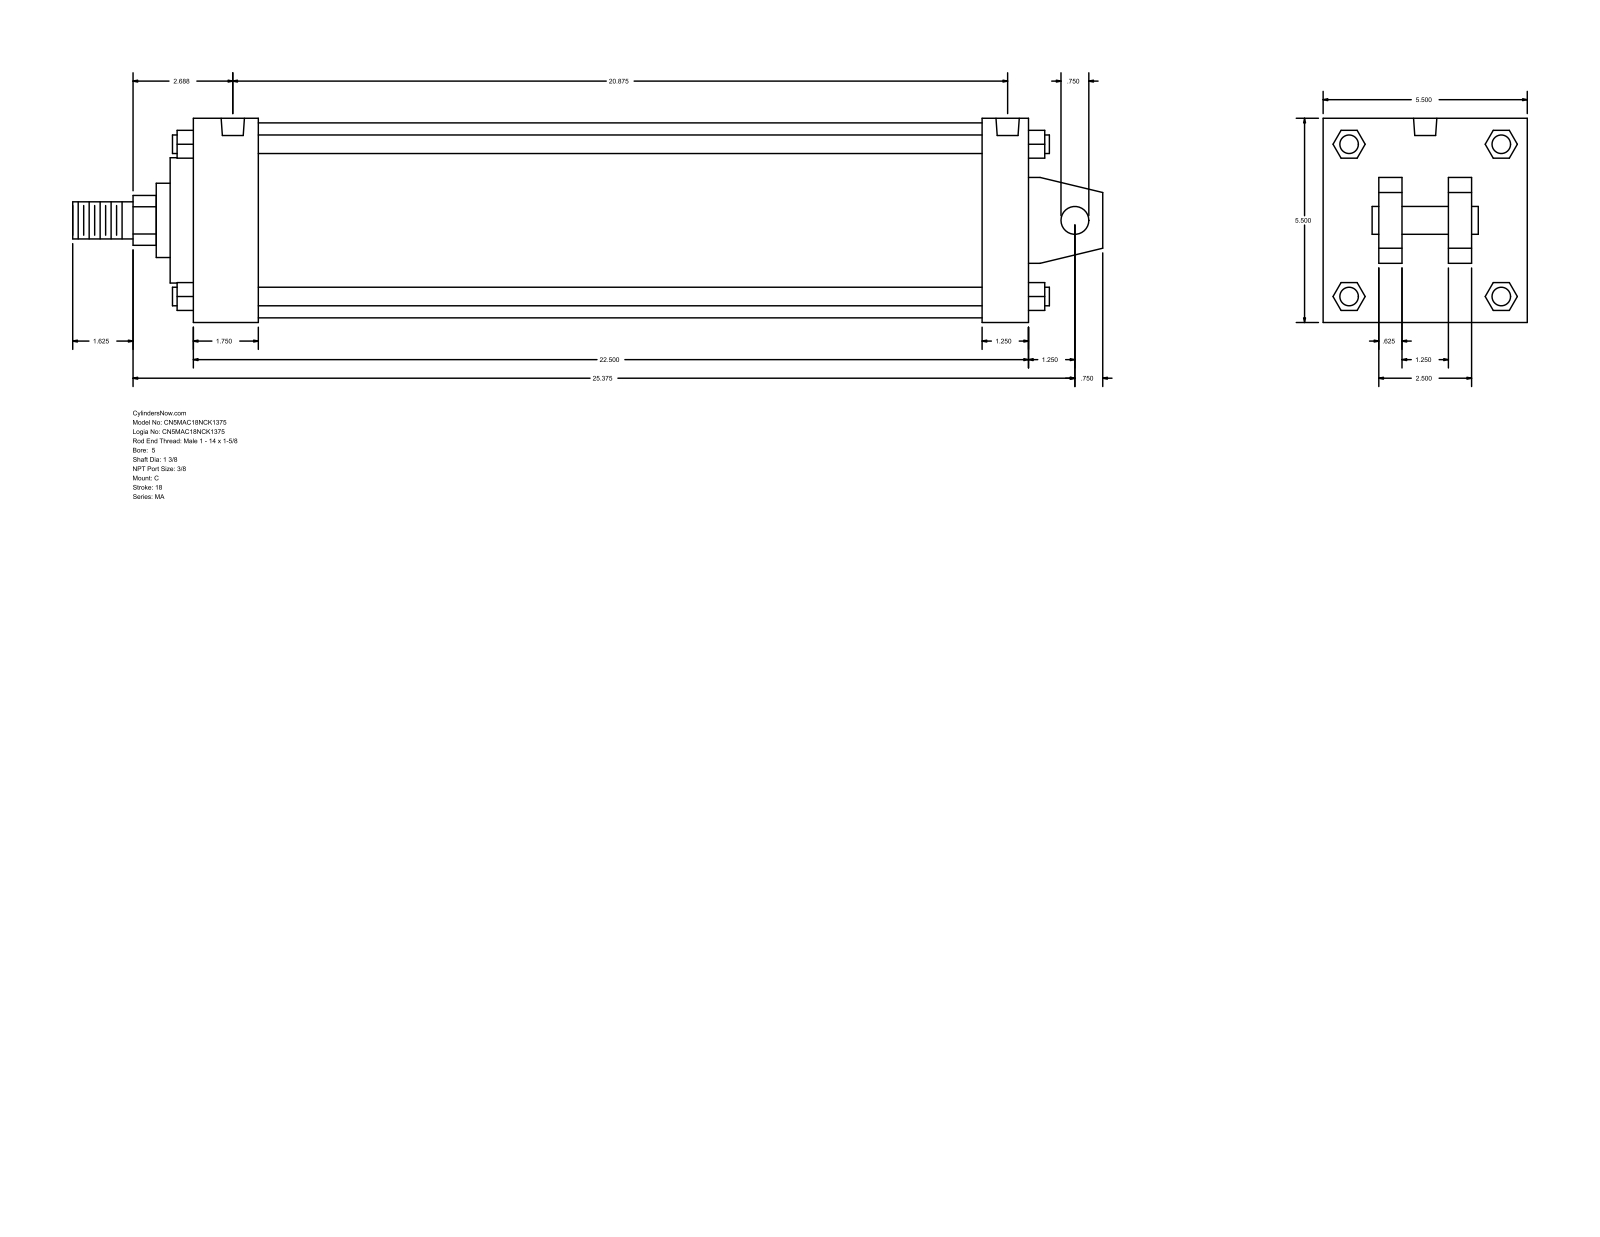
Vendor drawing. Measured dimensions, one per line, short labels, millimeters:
name: MA_C__0500_1.375
written by: GSSL Pune (CONFIG_CONTROL_DESIGN)
unit: mm
bodies: 0 solids, 141 faces (109 planar, 32 cylindrical, 0 other)
size: 704.85 × 139.7 × 139.7
holes: 4× ⌀11.11, 2× ⌀15.93
bosses: 4× ⌀12.7, 1× ⌀133.35, 1× ⌀85.72, 1× ⌀50.8, 1× ⌀34.92, 1× ⌀25.4, 1× ⌀19.05
rounds: 1× R17.06
face distances: 139.7, 571.5, 15.87, 539.75, 31.75, 44.45, 495.3, 527.05, 53.97, 38.1
hole spacings: 520.7, 4.76, 4.77, 525.46, 525.47, 530.23
